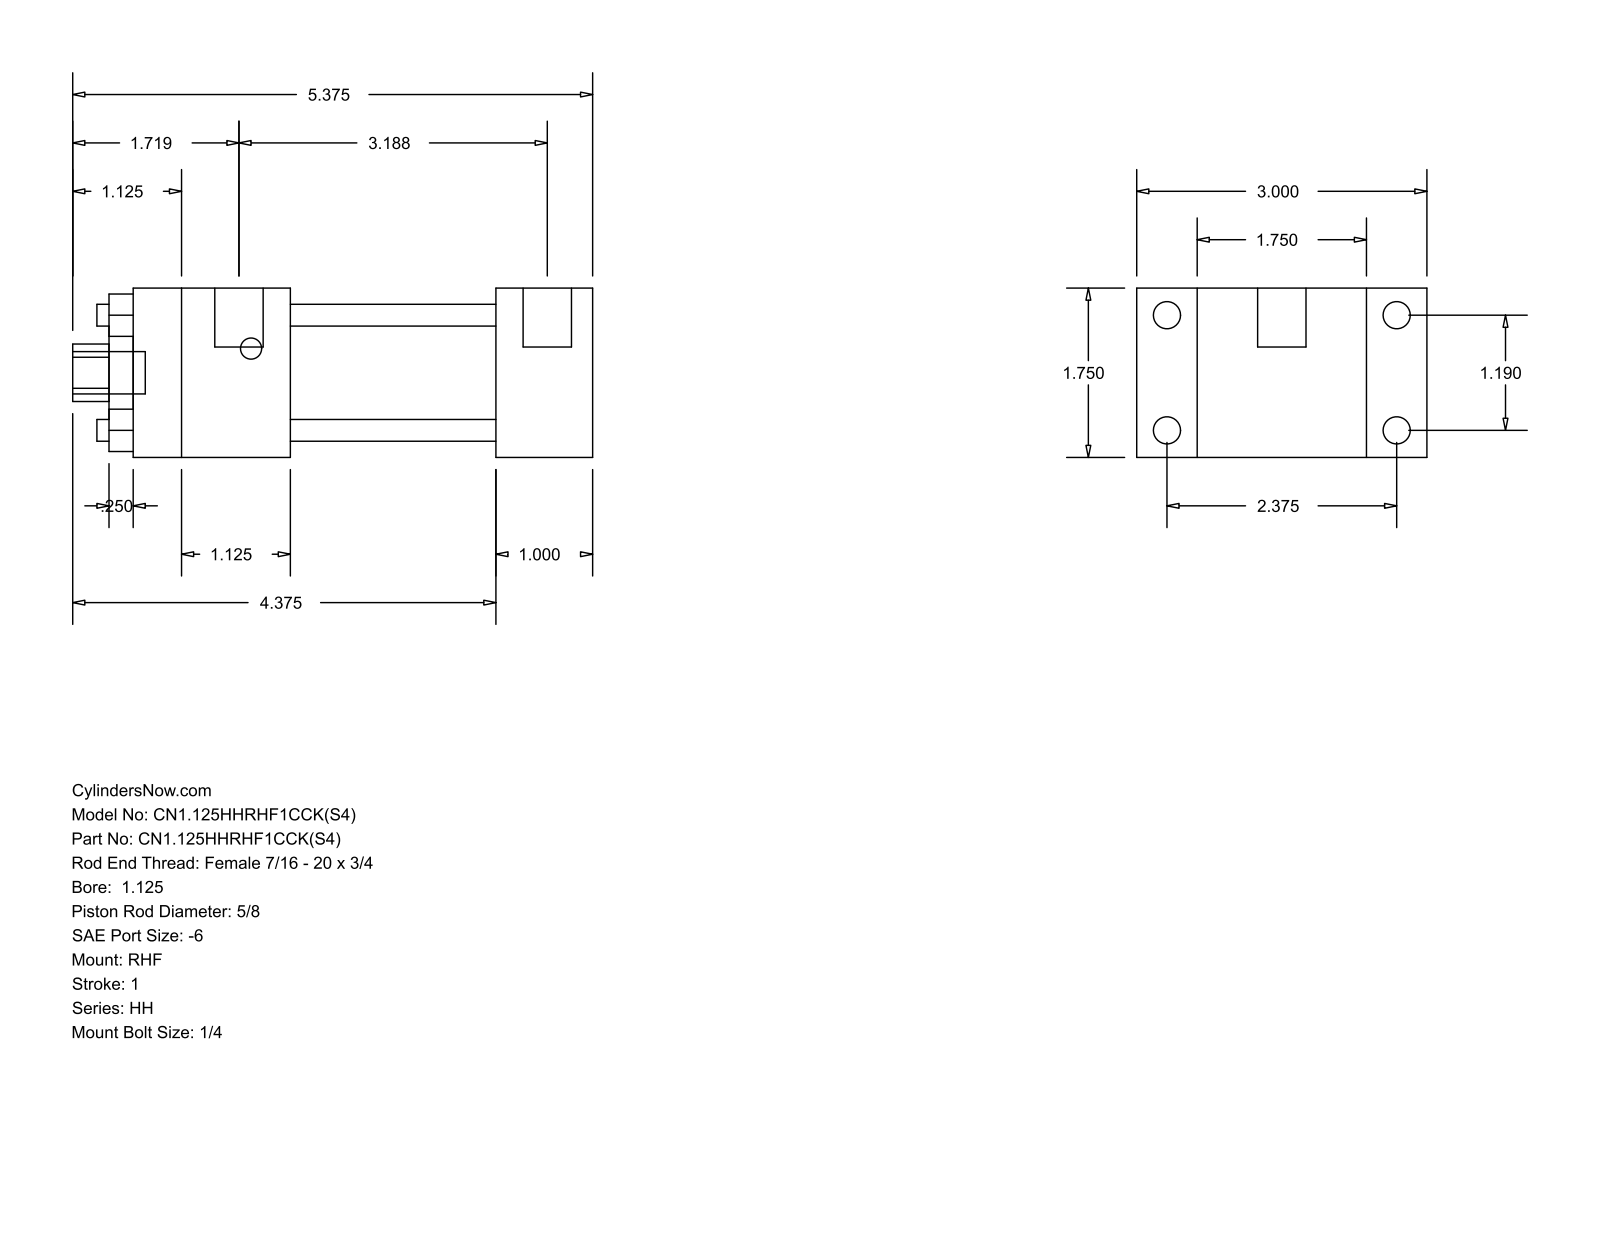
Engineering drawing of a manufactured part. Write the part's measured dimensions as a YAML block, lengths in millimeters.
part_name: "HH_RHF__0112_0.625"
step_written_by: "GSSL Pune (CONFIG_CONTROL_DESIGN)"
units: millimeters
bodies: {solids: 0, faces: 88, planar: 60, cylindrical: 28, other: 0}
overall_size: [136.53, 76.2, 44.45]
round_holes:
  - {diameter: 5.71, count: 4}
  - {diameter: 15.88, count: 1}
  - {diameter: 28.57, count: 1}
  - {diameter: 34.92, count: 1}
round_bosses_or_shafts:
  - {diameter: 7.14, count: 4}
  - {diameter: 5.56, count: 4}
  - {diameter: 12.7, count: 2}
  - {diameter: 11.11, count: 1}
partial_cylinders:
  - {radius: 7.54, count: 1}
face_to_face_distances: [44.46, 15.87, 60.33, 25.41, 76.2, 53.97, 79.38, 41.27, 95.24, 120.65]
hole_center_spacings: [21.37, 30.22, 42.74]
